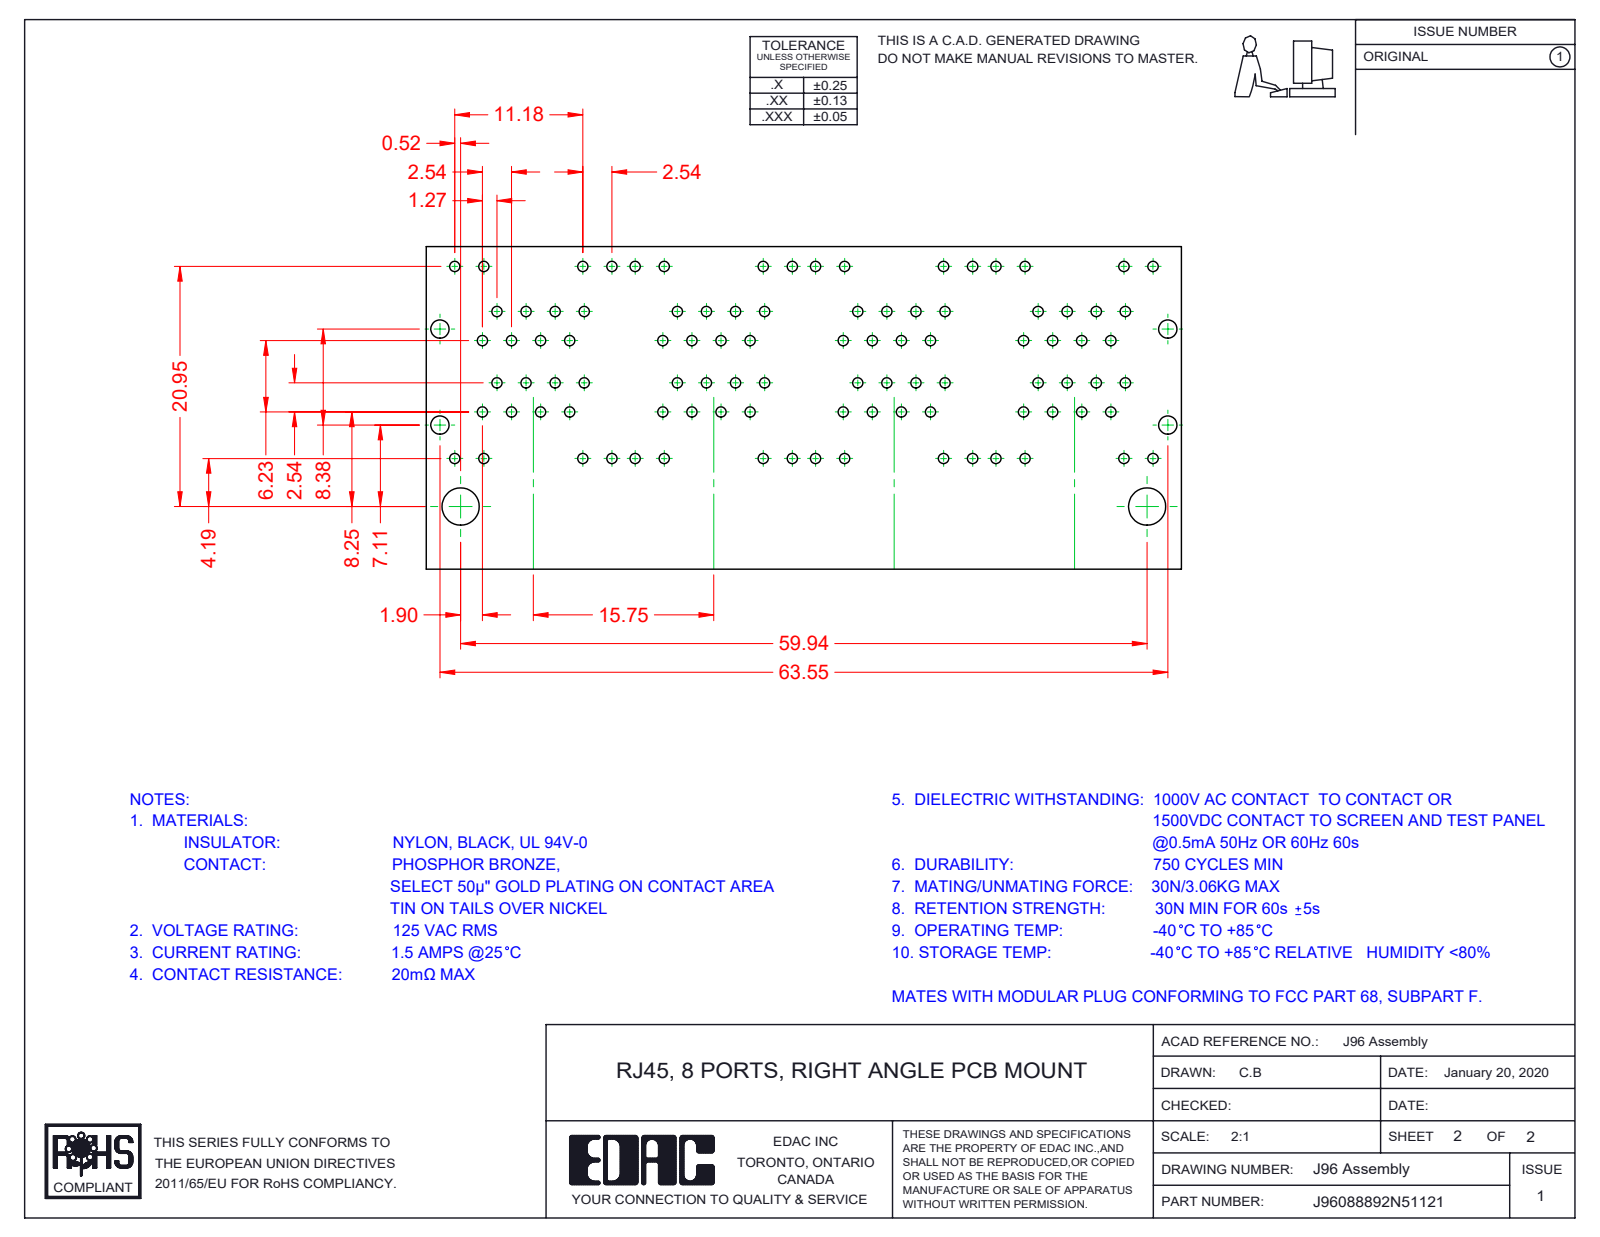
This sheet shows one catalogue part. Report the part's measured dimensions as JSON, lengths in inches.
{"part_name": "96 Contacts Upper; J96088892N51121; 96 LED LH Lower_5-Green-Yellow; 96 Shield_8 Ports LED - No EMI (+8 more)", "step_written_by": "SolidWorks 2016 (CONFIG_CONTROL_DESIGN)", "units": "inches", "bodies": {"solids": 96, "faces": 7658, "planar": 6069, "cylindrical": 1323, "other": 266}, "overall_size": [2.522, 1.165, 1.129], "volume_in3": 1.474, "surface_area_in2": 98.67, "round_holes": [[0.067, 3]], "round_bosses_or_shafts": [[0.066, 3]], "partial_cylinders_radius": [[0.01, 124], [0.014, 73], [0.039, 72], [0.02, 49], [0.036, 32], [0.008, 21], [0.028, 11], [0.009, 8]], "face_to_face_distances": [0.62, 0.014, 0.392, 0.046, 0.063, 0.021, 0.393, 0.401, 0.499, 0.133], "hole_center_spacings": [0.62, 1.24]}
